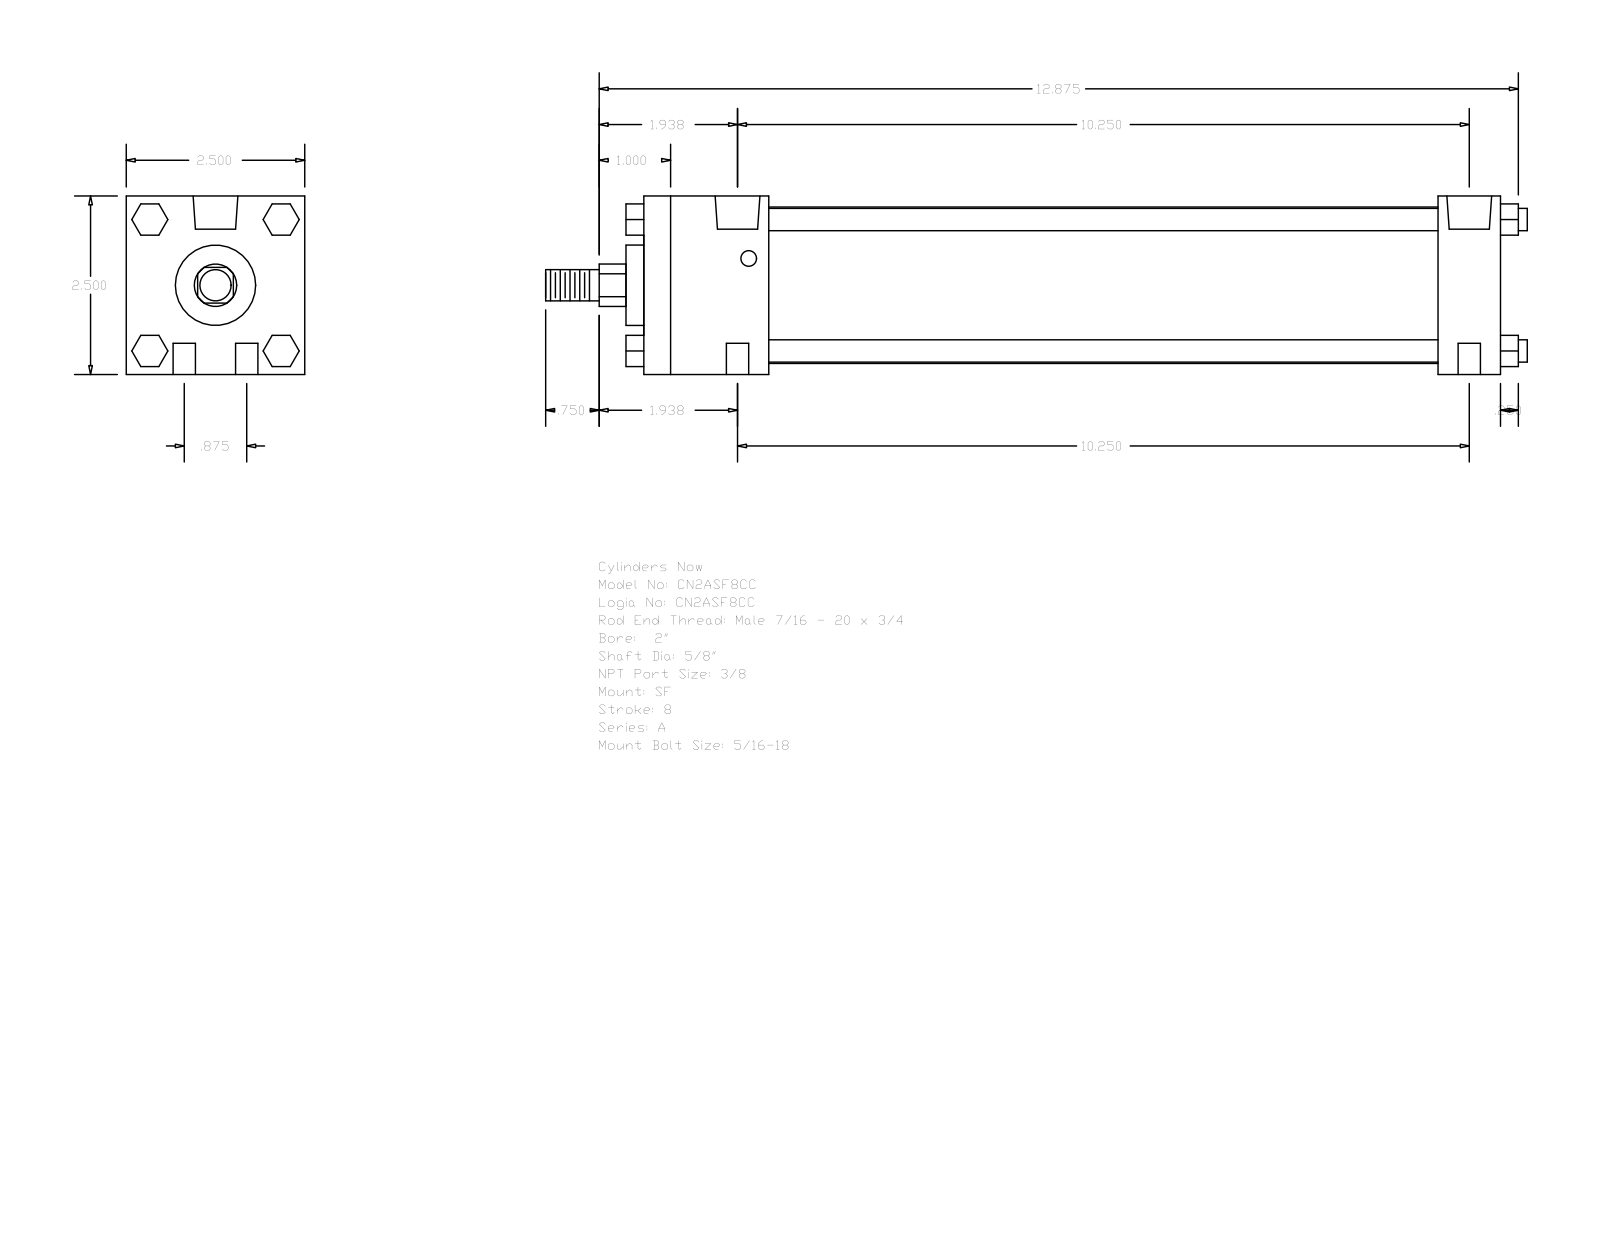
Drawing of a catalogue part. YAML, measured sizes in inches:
part_name: "A_SF__0200_0.625"
step_written_by: "GSSL Pune (CONFIG_CONTROL_DESIGN)"
units: inches
bodies: {solids: 0, faces: 124, planar: 94, cylindrical: 30, other: 0}
overall_size: [13.75, 2.5, 2.5]
round_holes:
  - {diameter: 0.313, count: 4}
  - {diameter: 0.219, count: 2}
  - {diameter: 0.627, count: 2}
round_bosses_or_shafts:
  - {diameter: 0.313, count: 4}
  - {diameter: 2.19, count: 1}
  - {diameter: 1.125, count: 1}
  - {diameter: 0.625, count: 1}
  - {diameter: 0.437, count: 1}
partial_cylinders:
  - {radius: 0.297, count: 1}
face_to_face_distances: [2.5, 12, 11.125, 0.875, 1.75, 9.375, 10.25, 2, 0.25, 11.375]
hole_center_spacings: [0.437, 10.259, 10.25, 0.875, 10.287, 9.937]
